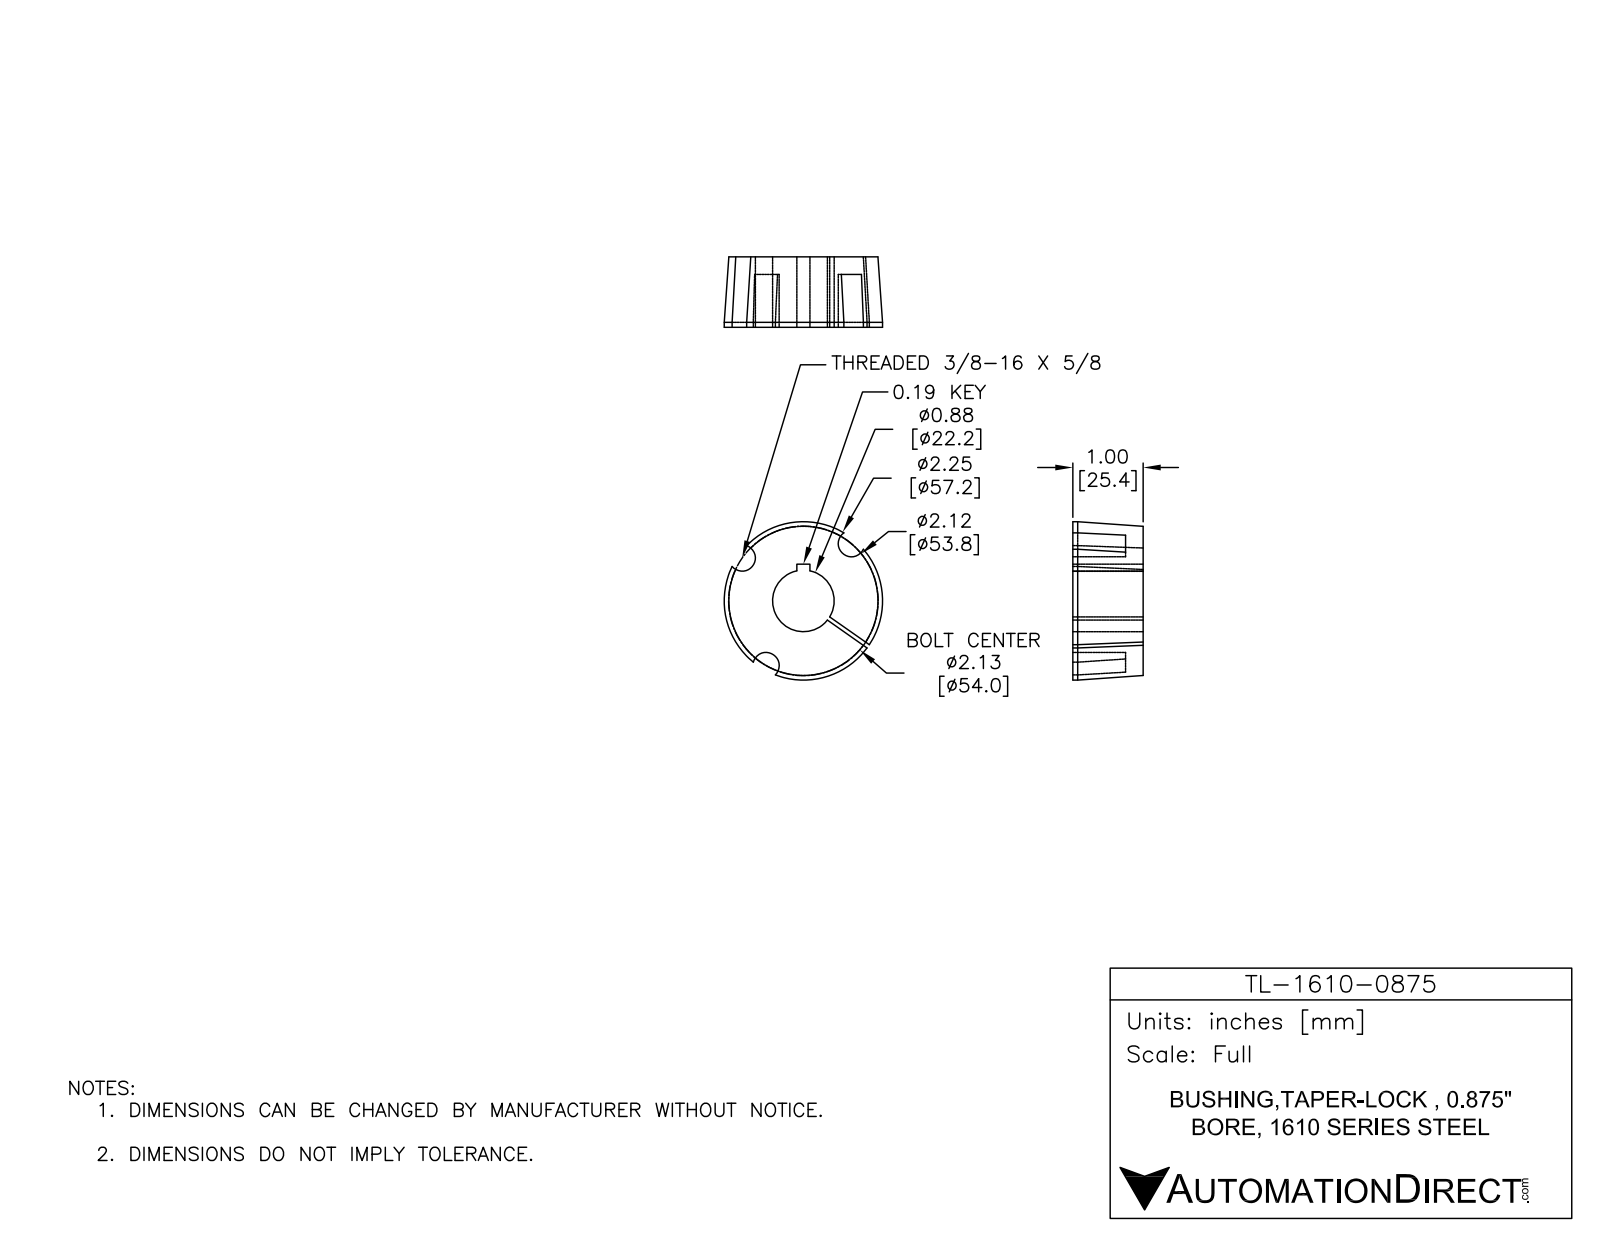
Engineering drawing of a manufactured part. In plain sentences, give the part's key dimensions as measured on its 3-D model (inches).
The part is named "TL-1610-0875". Its 3-D file was written by "SolidWorks 2014 (AUTOMOTIVE_DESIGN)". It is 1 solid with 25 faces: 9 planar, 13 cylindrical and 3 other. Overall it measures 2.25 by 2.25 by 1 inches. Its volume is 2.945 cubic inches and its surface area 17.7 square inches. Round holes: 1 of diameter 0.875. Round bosses or shafts: 1 of diameter 2.25. Partial cylindrical surfaces (rounded edges, fillets, slot ends): 3 of radius 0.188. The main face-to-face distances are 1, 0.057, 0.25, 0.75, 0.187.
